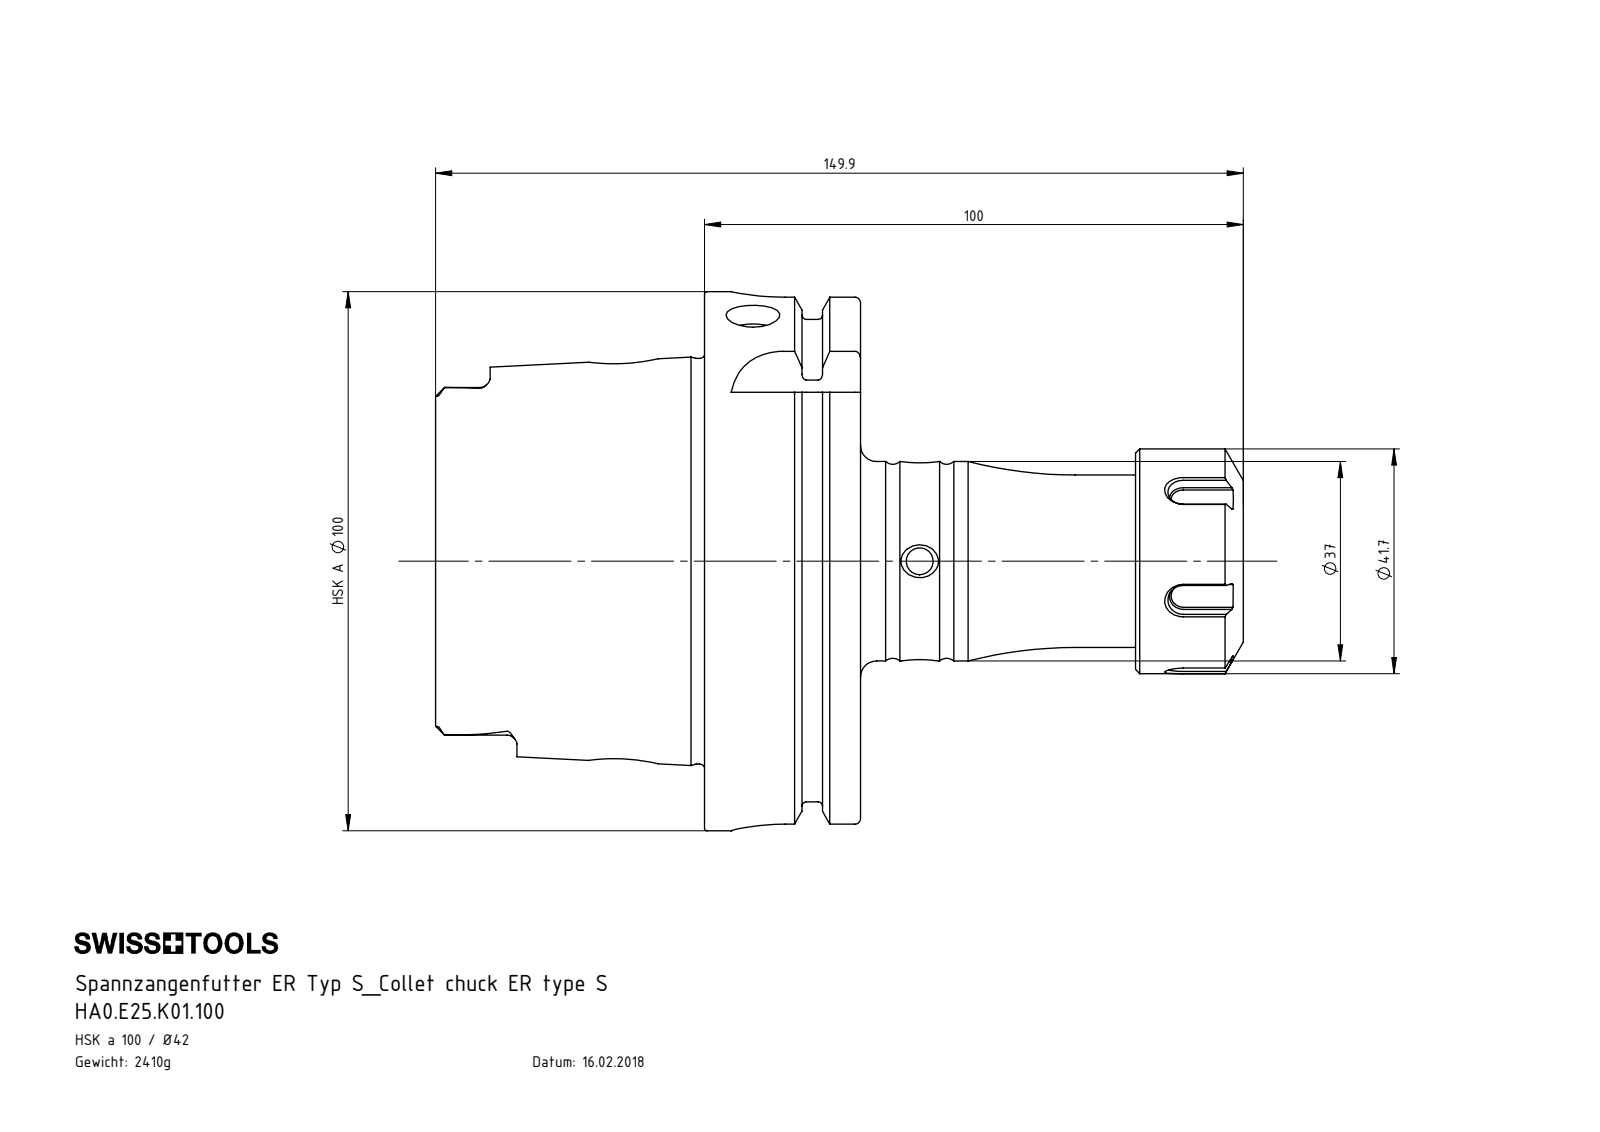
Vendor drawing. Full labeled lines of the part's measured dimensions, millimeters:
Part name (STEP PRODUCT): HA0-E25.K01.100_B_Fertigbearbeitung; E25-ER1.001.020; ERU-AN5.K01.020_A; HA0.E25.K01.100
STEP written by: SolidWorks 2017 (CONFIG_CONTROL_DESIGN)
Units: millimetres
Bodies: 3 solids, 348 faces (125 planar, 85 cylindrical, 138 other)
Overall size (bounding box): 149.9 × 100 × 100
Volume: 306 947 mm³ · Surface area: 66 485 mm²
Round holes (diameter × count): ⌀10 ×3, ⌀5 ×2, ⌀12 ×2, ⌀6 ×1, ⌀11 ×1, ⌀18 ×1, ⌀20.9 ×1, ⌀22.5 ×1, ⌀26 ×1, ⌀30.5 ×1, ⌀32.5 ×1, ⌀53 ×1
Round bosses / shafts (diameter × count): ⌀100 ×1, ⌀91.95 ×1, ⌀75.26 ×1, ⌀41.7 ×1, ⌀37 ×1, ⌀32 ×1
Partial cylindrical surfaces — rounded edges, fillets, slot ends (radius × count): R1.9 ×6, R4.88 ×4, R10 ×4, R12.17 ×2
Main face-to-face distances: 28.95, 12.45, 16.5, 49.9, 62.35, 78.85, 129.9, 80, 67.55, 51.05
Hole centre spacings: 32.95, 54.95
